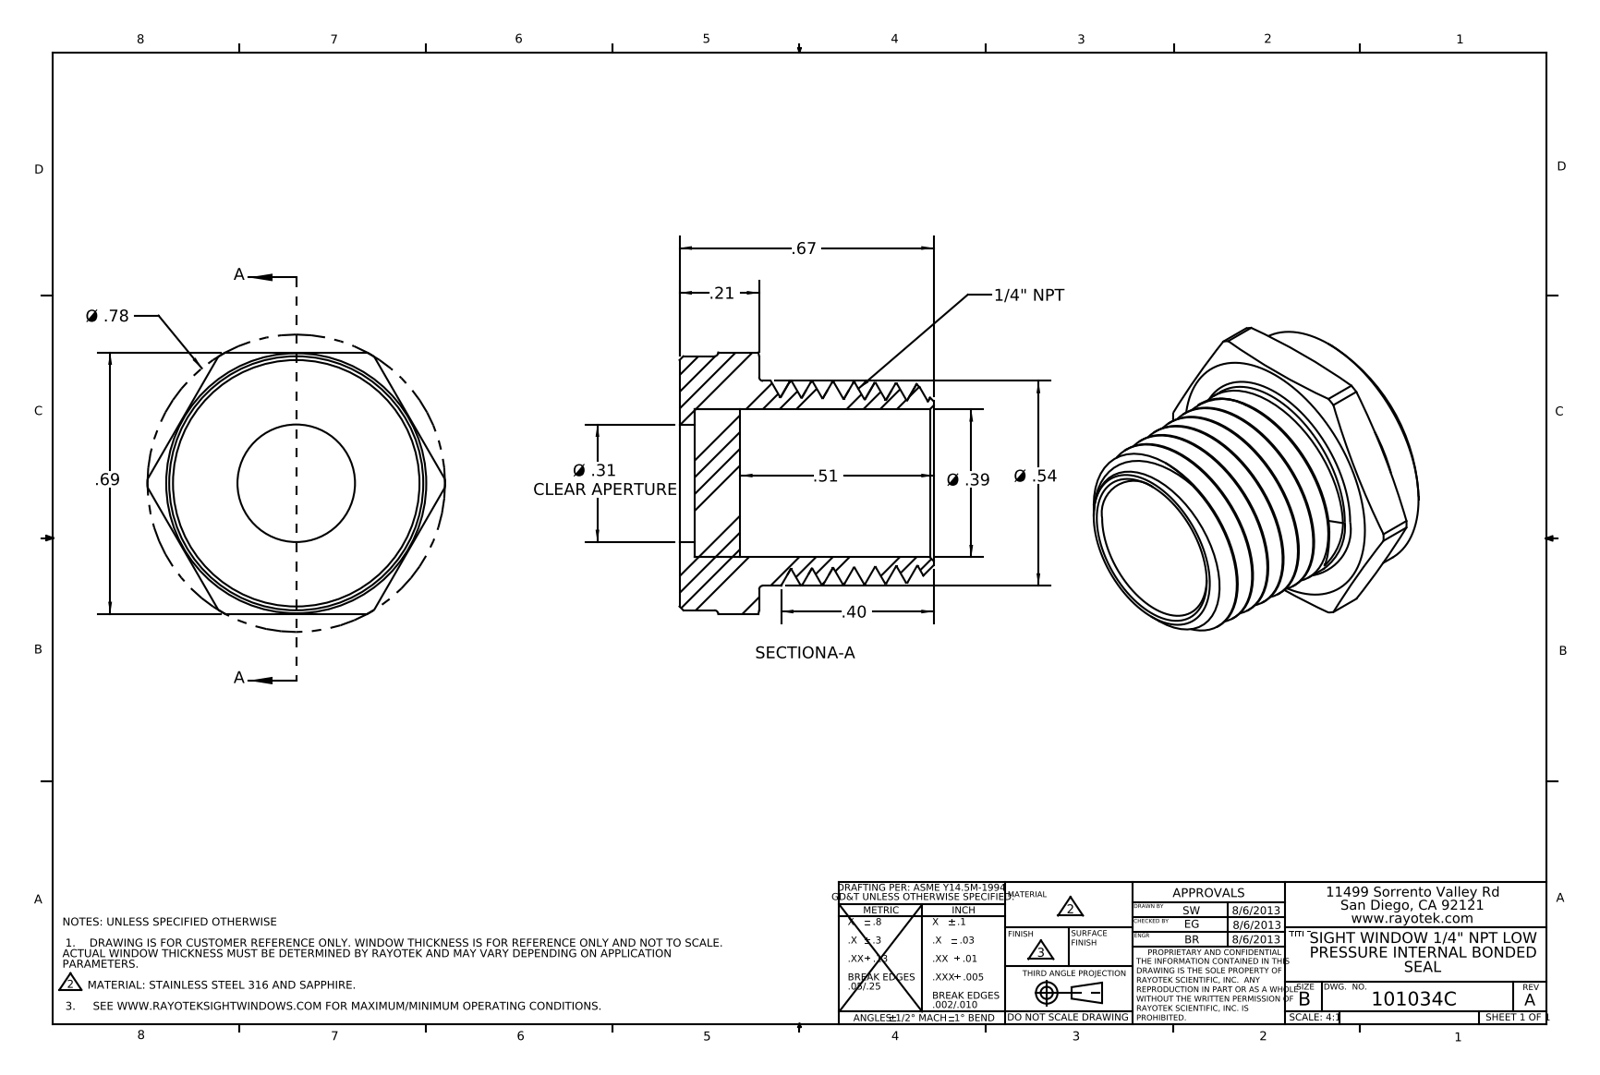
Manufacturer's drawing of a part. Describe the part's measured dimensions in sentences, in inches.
The part is named "403034". Its 3-D file was written by "SolidWorks 2012 (AUTOMOTIVE_DESIGN)". It is 2 solids with 64 faces: 15 planar, 18 cylindrical and 31 other. Overall it measures 0.785 by 0.69 by 0.67 inches. Its volume is 0.104 cubic inches and its surface area 3.476 square inches. Round holes: 1 of diameter 0.31, 1 of diameter 0.39. Round bosses or shafts: 1 of diameter 0.67, 1 of diameter 0.54. Partial cylindrical surfaces (rounded edges, fillets, slot ends): 1 of radius 0.392. The main face-to-face distances are 0.04, 0.16, 0.12, 0.69, 0.21, 0.17, 0.05, 0.67, 0.63, 0.51.
